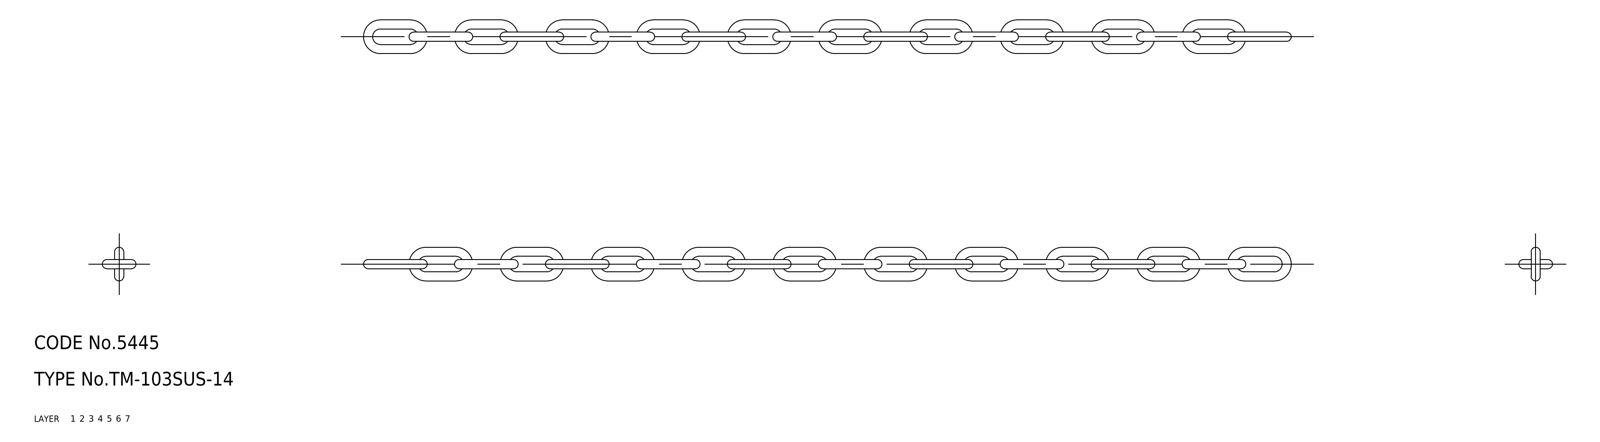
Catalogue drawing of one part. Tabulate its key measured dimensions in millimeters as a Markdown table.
| quantity | value |
| --- | --- |
| part name | chain; TM_103SUS_14_11449_36 |
| STEP written by | CADfix (AUTOMOTIVE_DESIGN) |
| units | millimeters |
| bodies | 20 solids, 160 faces (0 planar, 0 cylindrical, 160 other) |
| overall size | 204 × 7.4 × 7.4 |
| volume | 1 895 mm³ |
| surface area | 3 791 mm² |
